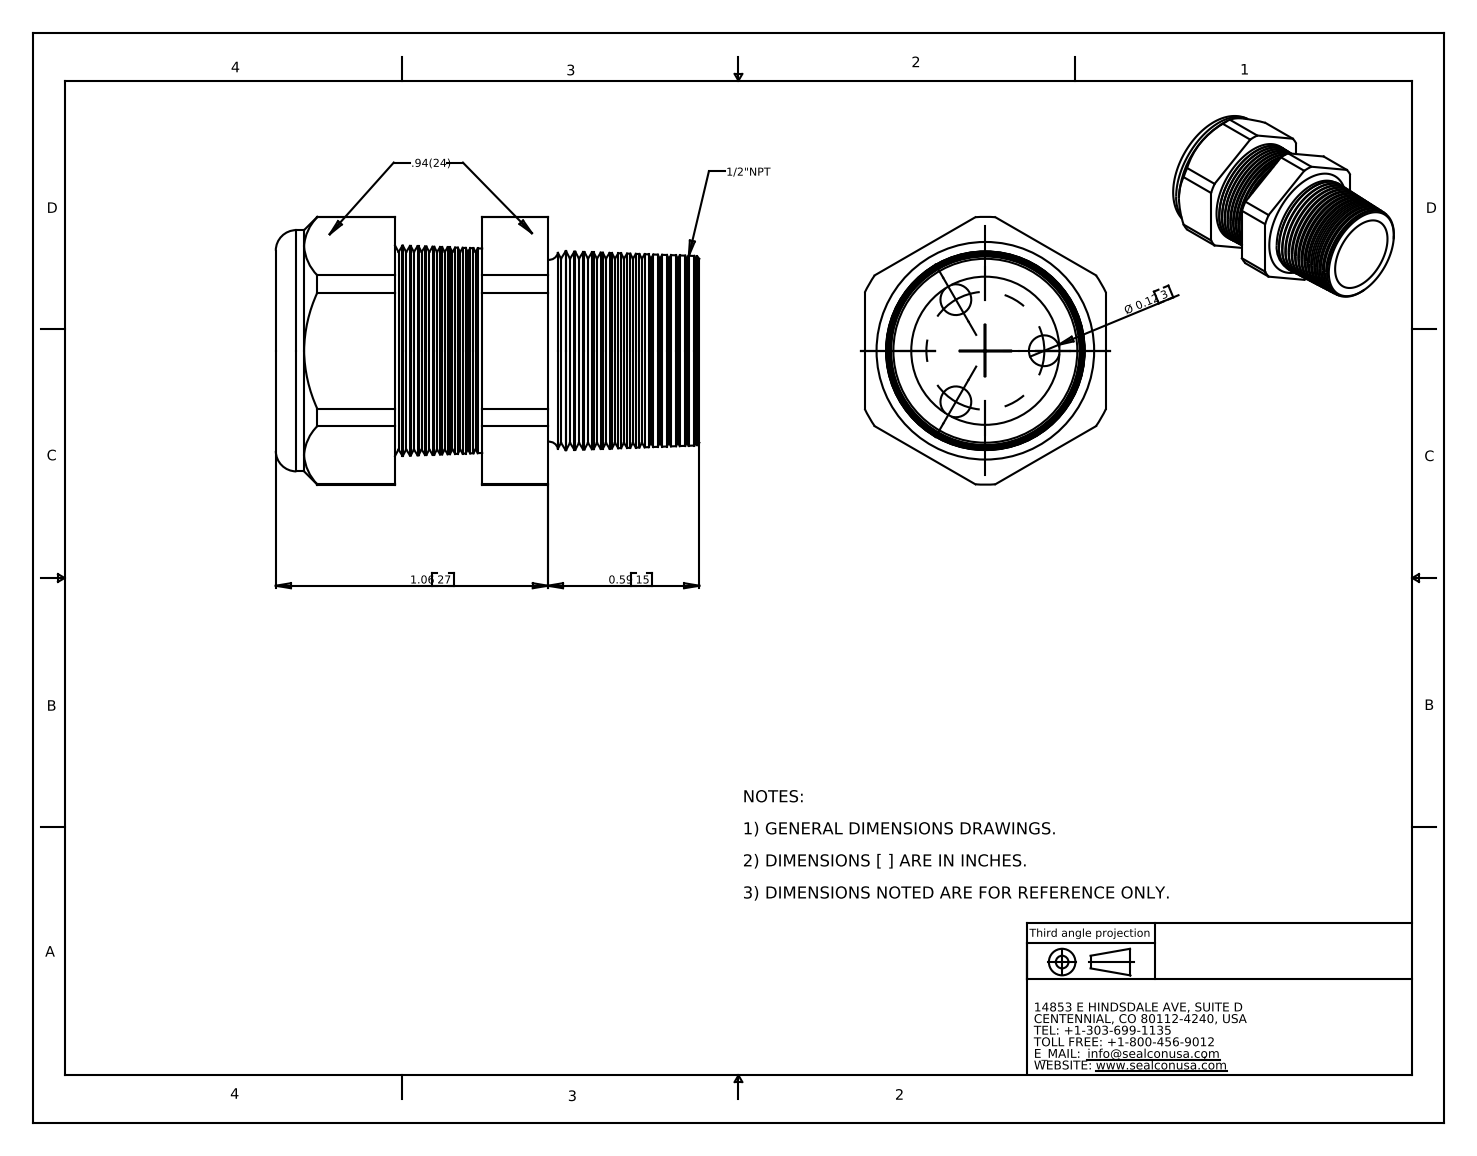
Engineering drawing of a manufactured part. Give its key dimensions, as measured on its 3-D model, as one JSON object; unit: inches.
{"part_name": "CD13N5-GY", "step_written_by": "SolidWorks 2007 (CONFIG_CONTROL_DESIGN)", "units": "inches", "bodies": {"solids": 2, "faces": 210, "planar": 20, "cylindrical": 26, "other": 164}, "overall_size": [1.57, 1.043, 0.94], "volume_in3": 0.567, "surface_area_in2": 11.62, "round_holes": [[0.12, 3], [0.58, 1], [0.6, 1]], "round_bosses_or_shafts": [[0.94, 1]], "partial_cylinders_radius": [[0.522, 1]], "face_to_face_distances": [0.94, 0.454, 0.115, 0.34, 0.33, 0.444, 0.784, 0.02, 0.35, 0.465], "hole_center_spacings": [0.23, 0.398, 0.23, 0.398]}
